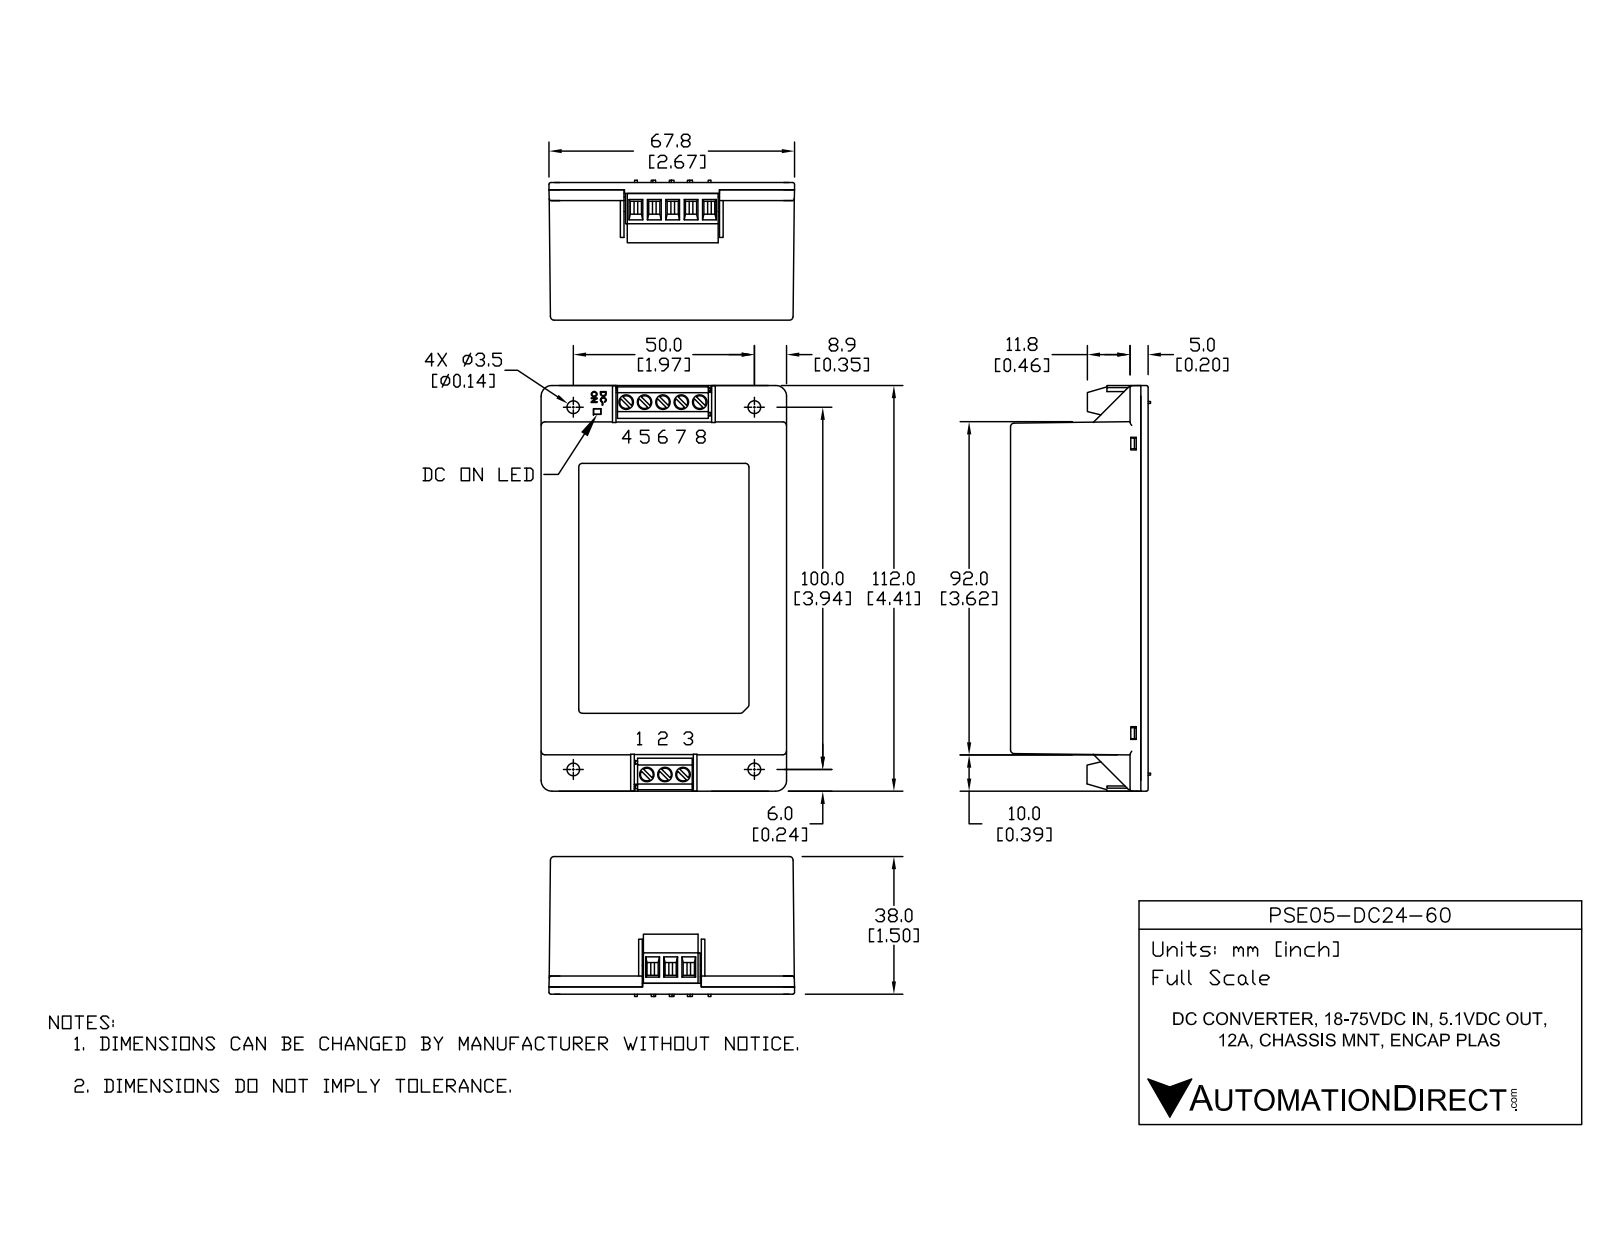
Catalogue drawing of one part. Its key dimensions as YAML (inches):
part_name: "PSE05-DC24-60"
step_written_by: "SolidWorks 2015 (AUTOMOTIVE_DESIGN)"
units: inches
bodies: {solids: 0, faces: 390, planar: 282, cylindrical: 89, other: 19}
overall_size: [4.446, 2.728, 1.459]
round_holes:
  - {diameter: 0.157, count: 10}
  - {diameter: 0.138, count: 4}
  - {diameter: 0.097, count: 1}
  - {diameter: 0.161, count: 1}
  - {diameter: 0.256, count: 1}
round_bosses_or_shafts:
  - {diameter: 0.059, count: 4}
  - {diameter: 0.197, count: 1}
partial_cylinders:
  - {radius: 0.039, count: 17}
  - {radius: 0.02, count: 8}
  - {radius: 0.085, count: 4}
  - {radius: 0.104, count: 4}
  - {radius: 0.118, count: 4}
  - {radius: 0.128, count: 3}
face_to_face_distances: [0.039, 0.039, 1.378, 1.339, 0.028, 0.04, 0.067, 1.311, 1.378, 1.338]
hole_center_spacings: [0.2, 0.4, 1.969, 4.021, 4.027, 0.197, 0.6, 3.937]
